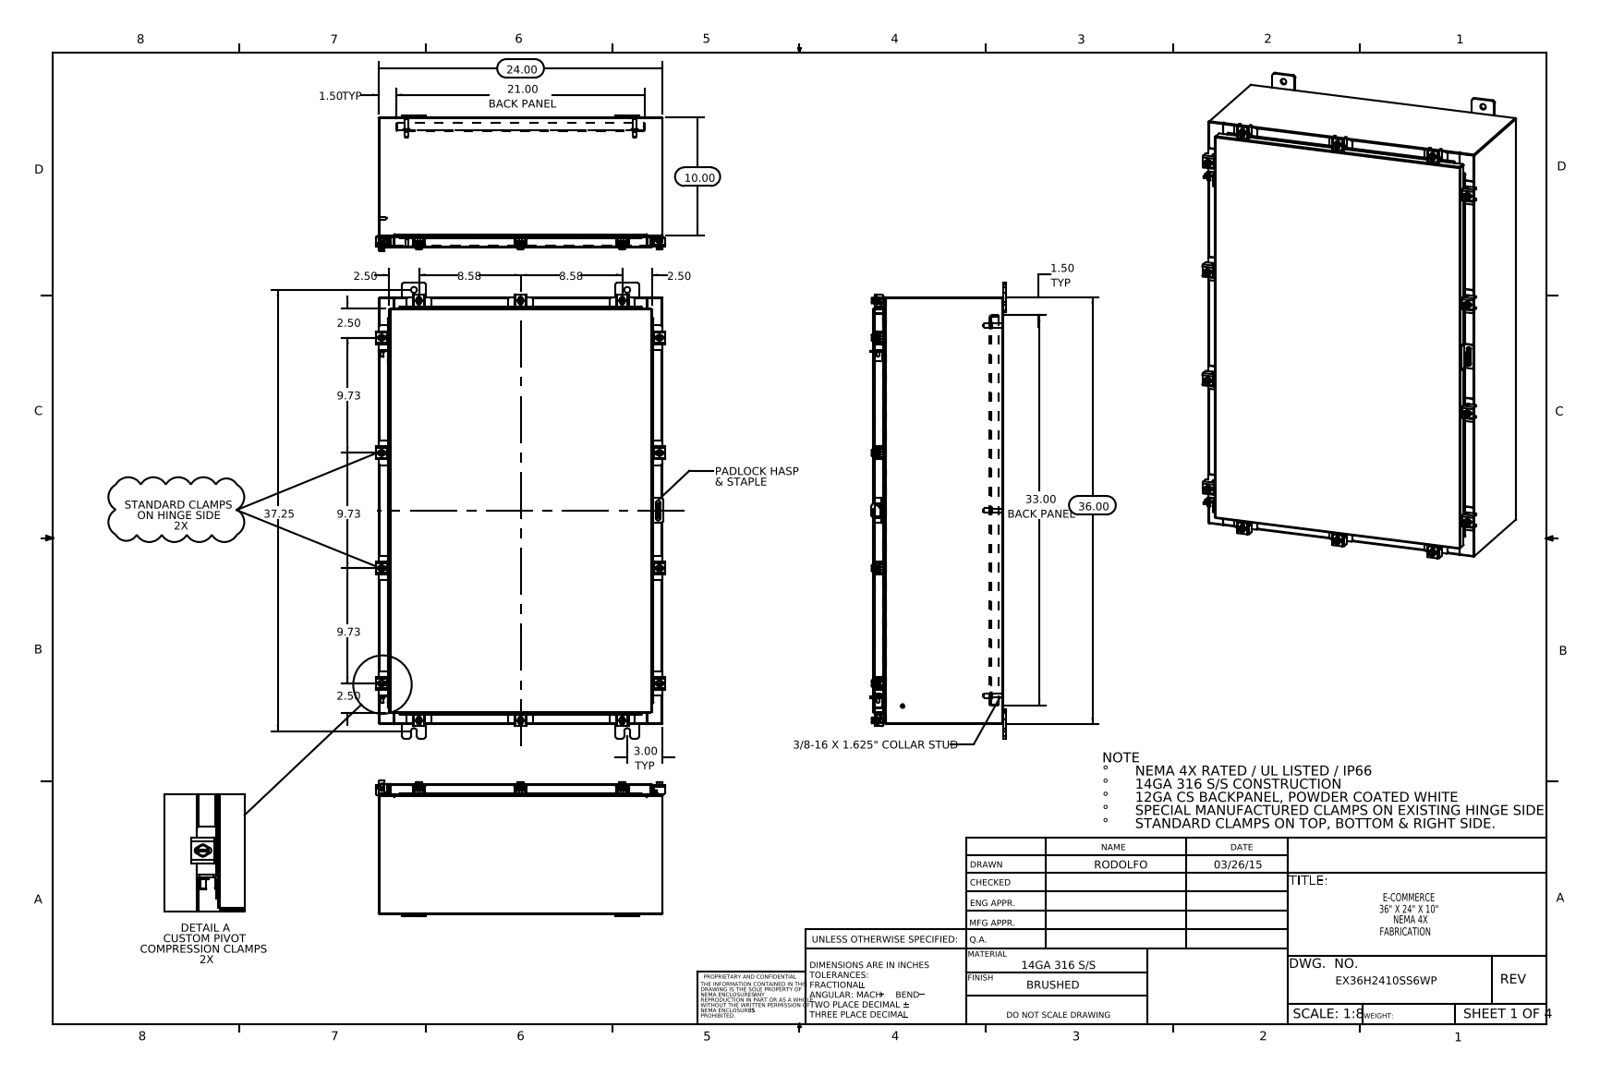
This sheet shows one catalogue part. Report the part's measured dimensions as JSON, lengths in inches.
{"part_name": "EX36H2410SS6WP Top; EX36H2410SS6WP Standard Clamps; EX36H2410SS6WP Cover; N-WMT04X30402202210-00 Clamp Top (+8 more)", "step_written_by": "SolidWorks 2014 (CONFIG_CONTROL_DESIGN)", "units": "inches", "bodies": {"solids": 93, "faces": 2322, "planar": 1221, "cylindrical": 905, "other": 196}, "overall_size": [38.5, 24.421, 11.453], "volume_in3": 327.4, "surface_area_in2": 8148, "round_holes": [[0.213, 14], [0.26, 14], [0.5, 10], [0.125, 1], [0.25, 1]], "round_bosses_or_shafts": [[0.5, 14], [0.25, 14], [0.399, 12], [0.625, 6], [0.375, 6], [0.33, 6], [0.315, 2], [0.236, 2]], "partial_cylinders_radius": [[0.06, 62], [0.141, 28], [0.013, 26], [0.12, 26], [0.19, 24], [0.088, 22], [0.09, 20], [0.05, 19]], "face_to_face_distances": [0.075, 10.9, 10.975, 10.826, 0.104, 23.925, 1, 1.075, 9.826, 9.9], "hole_center_spacings": [25.389, 2.347, 4.44, 5.299, 9.73, 10.964, 13.241, 14.744]}
